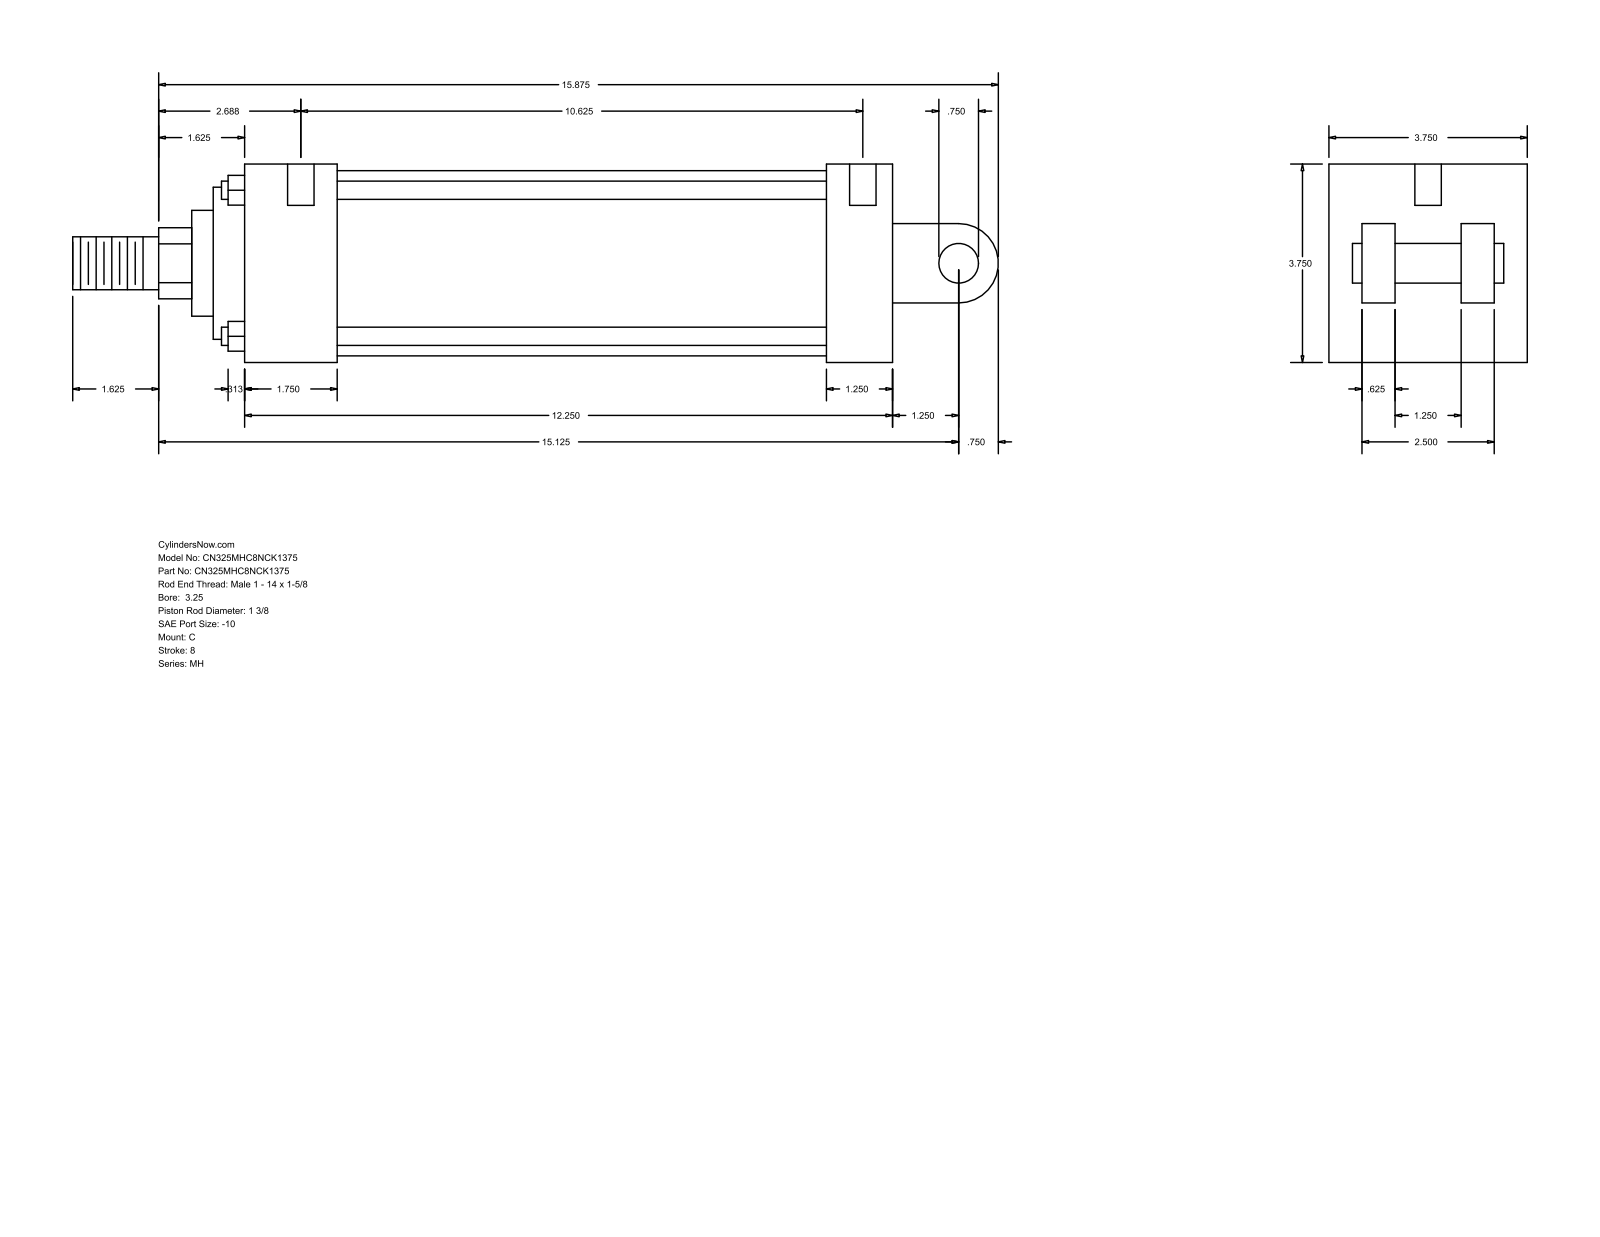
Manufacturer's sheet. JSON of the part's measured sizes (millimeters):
{"part_name": "MH_C__0325_1.375", "step_written_by": "GSSL Pune (CONFIG_CONTROL_DESIGN)", "units": "millimeters", "bodies": {"solids": 0, "faces": 101, "planar": 71, "cylindrical": 30, "other": 0}, "overall_size": [444.5, 95.25, 95.25], "round_holes": [[5.56, 4], [12.7, 2]], "round_bosses_or_shafts": [[8.76, 4], [88.9, 1], [73.03, 1], [50.8, 1], [34.92, 1], [25.4, 1], [19.05, 1]], "partial_cylinders_radius": [[17.06, 1], [19.05, 1]], "face_to_face_distances": [95.24, 15.87, 63.5, 311.16, 79.37, 31.74, 47.63, 44.45, 279.41, 234.96], "hole_center_spacings": [276.23, 1.59, 4.76, 269.88, 271.47, 274.64]}
